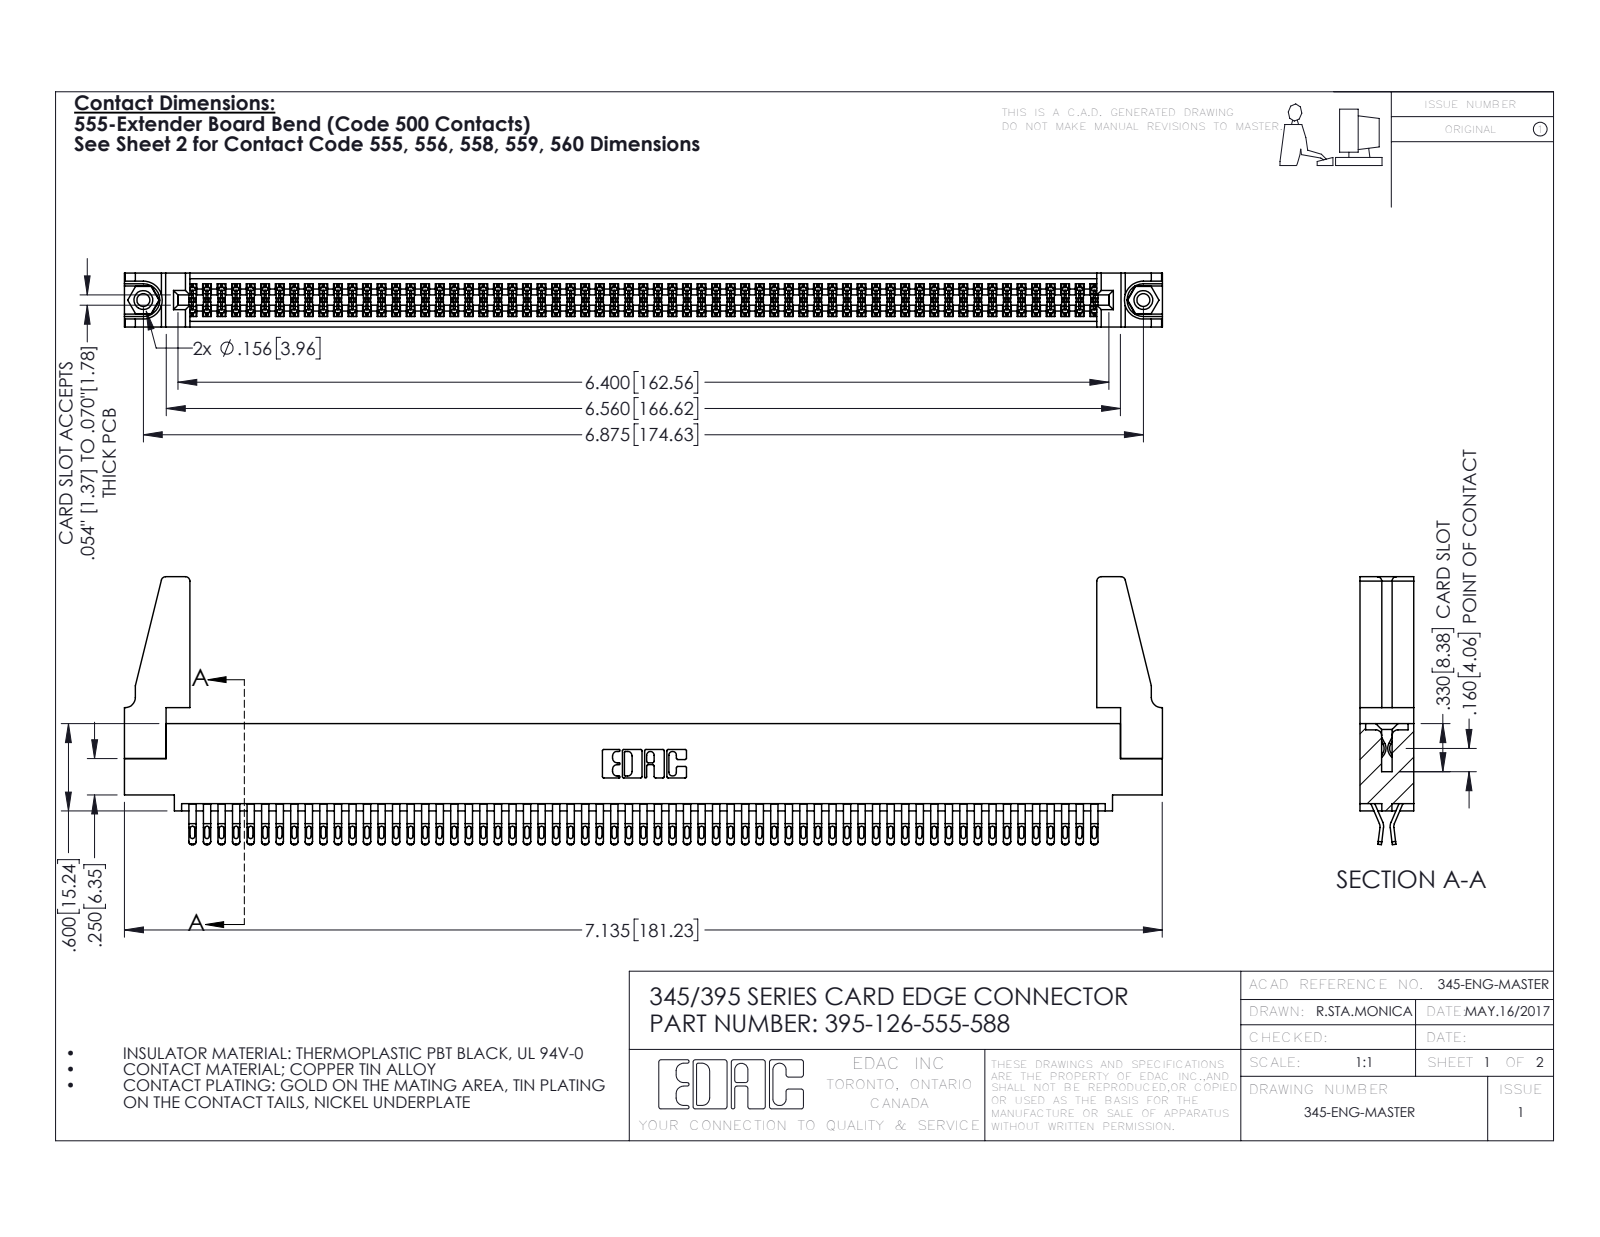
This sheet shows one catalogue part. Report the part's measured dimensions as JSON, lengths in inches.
{"part_name": "345-250-001_345-250-001-102; 345-292-001_555 Tail; 345-220-078_345-220-088; 345 Part_0.110 Offset - 0.156 Dia-TH (+1 more)", "step_written_by": "SolidWorks 2016 (CONFIG_CONTROL_DESIGN)", "units": "inches", "bodies": {"solids": 131, "faces": 7310, "planar": 4062, "cylindrical": 3232, "other": 16}, "overall_size": [7.136, 1.842, 0.37], "volume_in3": 1.303, "surface_area_in2": 49.04, "round_holes": [[0.089, 2], [0.125, 2], [0.156, 2], [0.064, 1]], "round_bosses_or_shafts": [[0.155, 2]], "partial_cylinders_radius": [[0.016, 315], [0.02, 252], [0.006, 189], [0.01, 22], [0.03, 8], [0.007, 6], [0.031, 6], [0.026, 3]], "face_to_face_distances": [0.072, 0.298, 0.37, 0.025, 0.2, 0.098, 0.272, 0.225, 0.175, 0.149], "hole_center_spacings": [0.27, 6.639, 6.875]}
